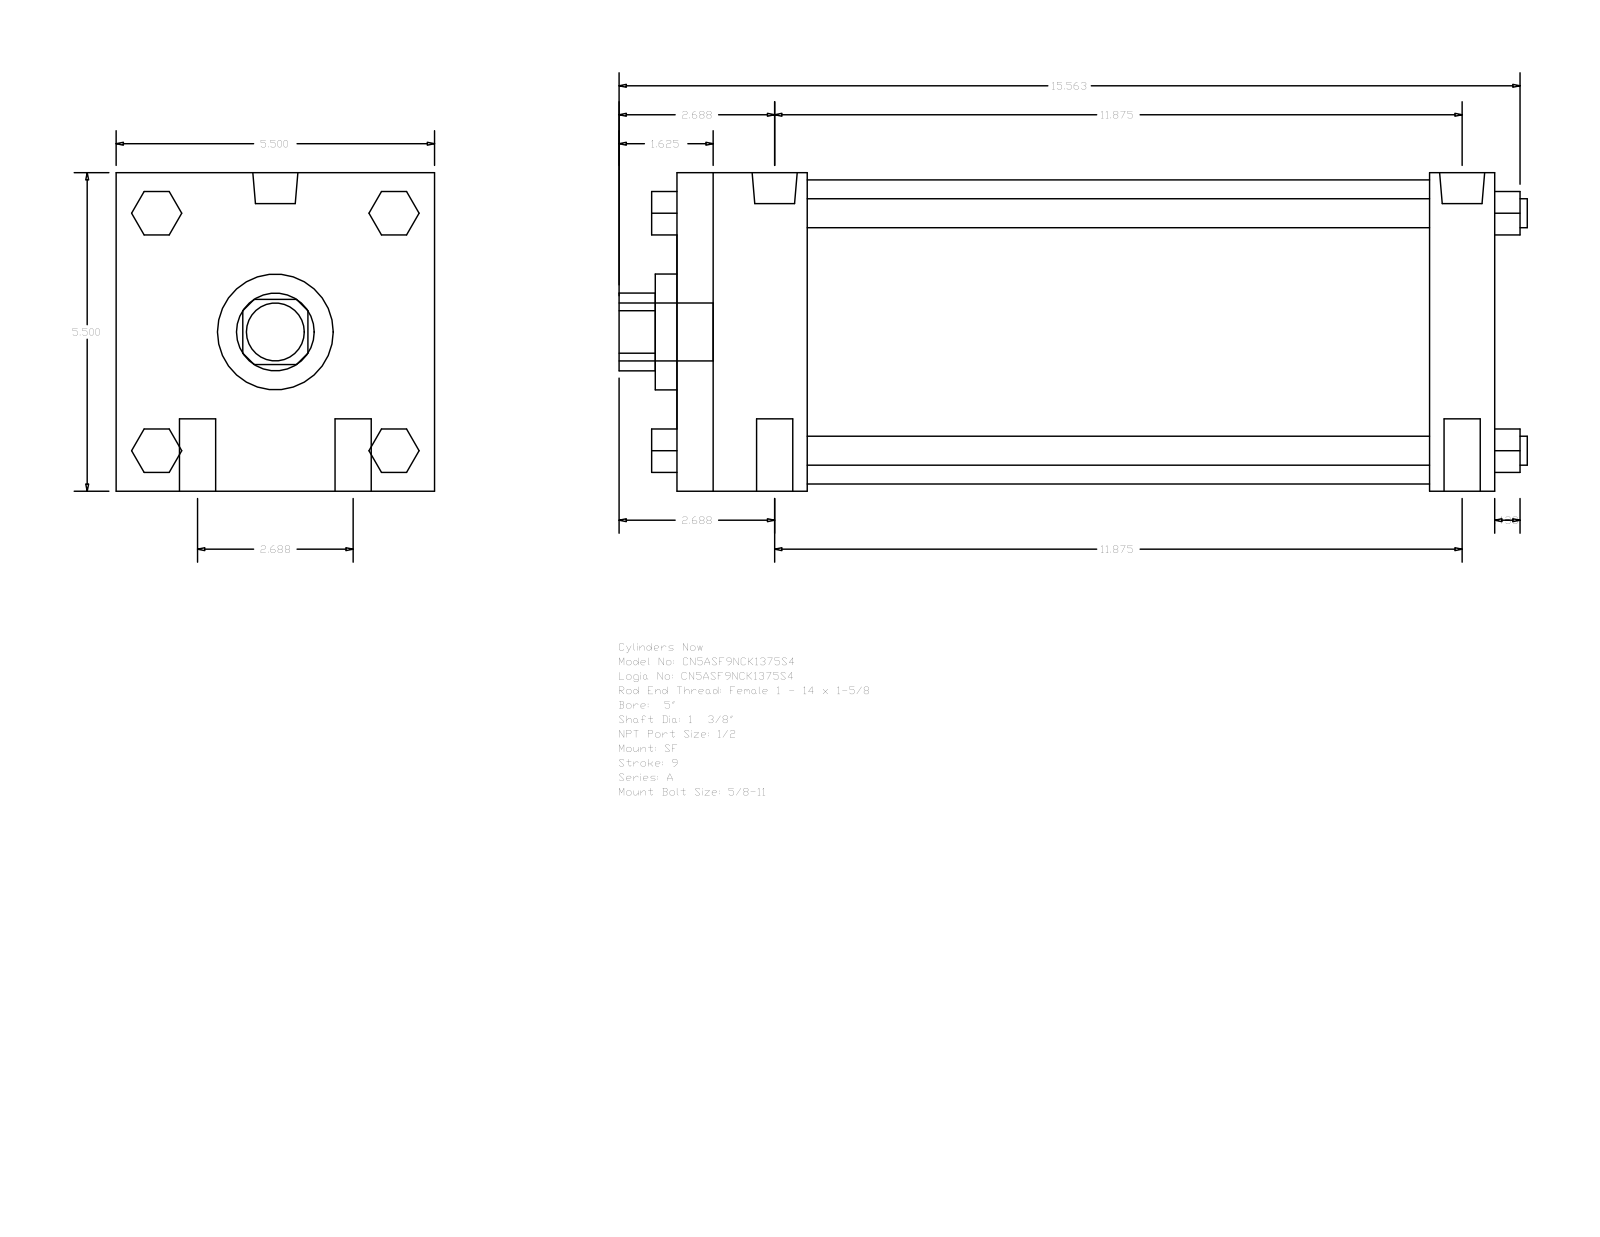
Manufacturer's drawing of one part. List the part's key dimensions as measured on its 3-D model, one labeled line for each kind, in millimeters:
Part name (STEP PRODUCT): A_SF__0500_1.375
STEP written by: GSSL Pune (CONFIG_CONTROL_DESIGN)
Units: millimetres
Bodies: 0 solids, 124 faces (94 planar, 30 cylindrical, 0 other)
Overall size (bounding box): 398.46 × 139.7 × 139.7
Round holes (diameter × count): ⌀34.92 ×1, ⌀50.8 ×1, ⌀133.35 ×1
Round bosses / shafts (diameter × count): ⌀15.88 ×4, ⌀12.7 ×4, ⌀19.77 ×2, ⌀8.73 ×2, ⌀25.4 ×1
Partial cylindrical surfaces — rounded edges, fillets, slot ends (radius × count): R17.06 ×1
Main face-to-face distances: 139.7, 358.78, 28.58, 57.15, 330.2, 273.05, 301.63, 19.05, 52.07, 90.18
